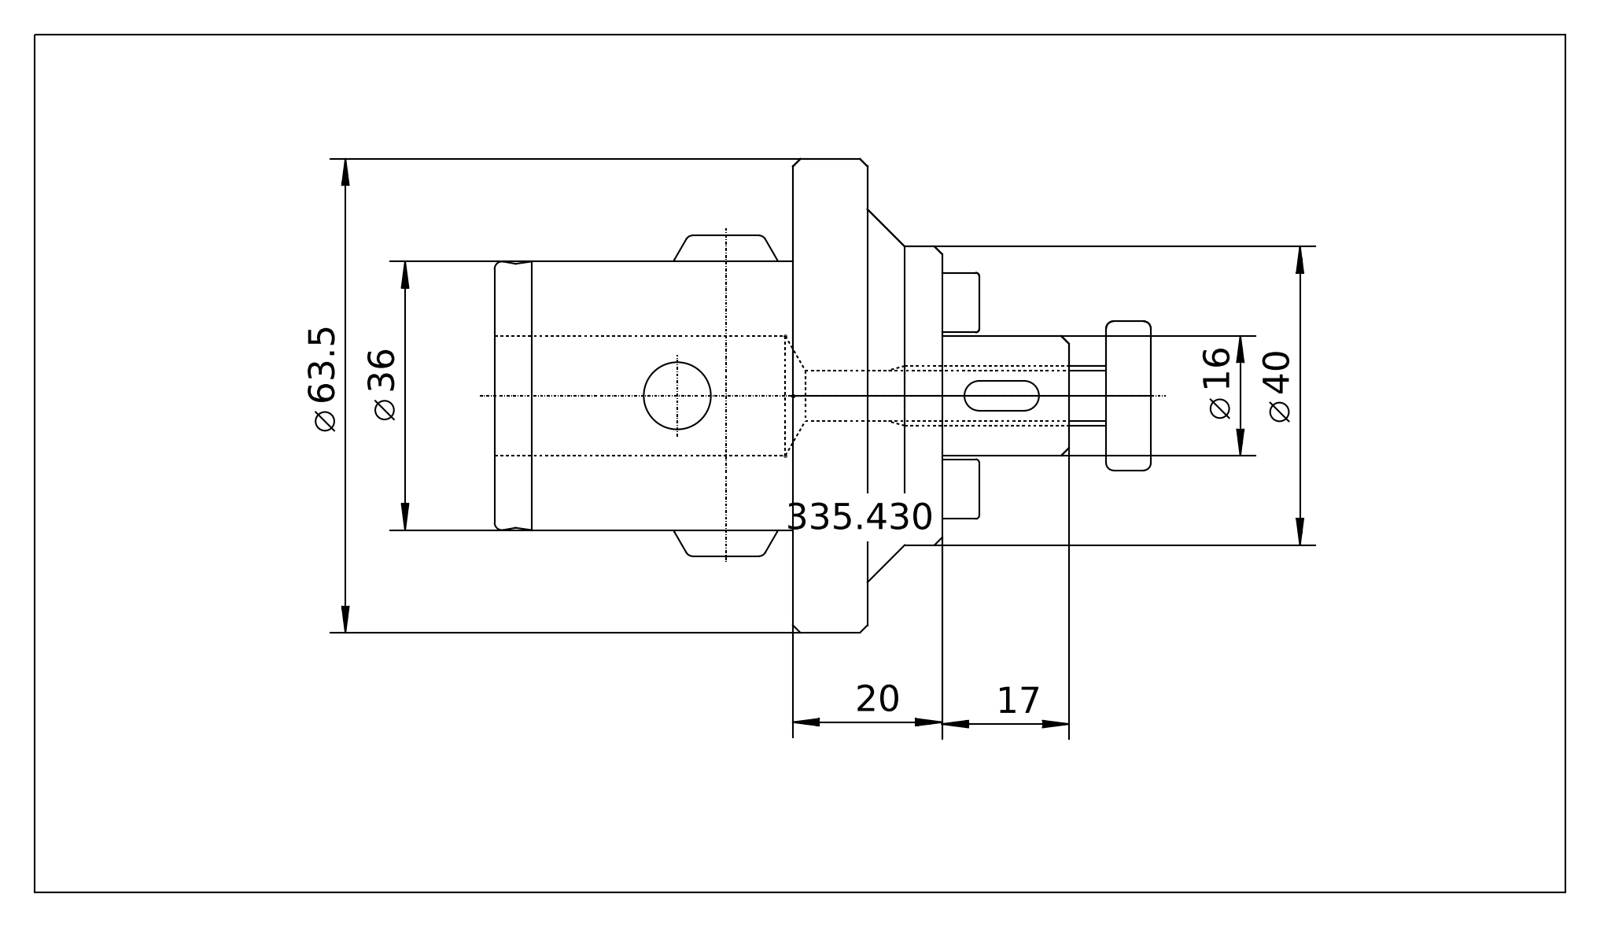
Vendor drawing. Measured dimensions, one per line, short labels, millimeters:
name: 335.430 Kaiser CKS6 X F16|690.703 Kaiser ETL FR16_M8_Standard-1;NONE; 335.430 Kaiser CKS6 X F16|690.703 Kaiser ETL FR16_M8_Standard;NONE; 335.430 Kaiser CKS6 X F16|691.605 Kaiser ETL MST 16 (Paar)_Standard;NONE; 335.430 Kaiser CKS6 X F16|691.600 Kaiser ETL FK 4 X 4_Standard;NONE (+3 more)
written by: ACIS (automotive_design)
unit: mm
bodies: 8 solids, 229 faces (71 planar, 74 cylindrical, 84 other)
size: 86.85 × 63.5 × 63.5
volume: 81 823 mm³; area: 24 643 mm²
holes: 2× ⌀2, 1× ⌀2.5, 1× ⌀3.2, 1× ⌀5.7, 1× ⌀6.75, 1× ⌀8.5, 1× ⌀9, 1× ⌀12, 1× ⌀14, 1× ⌀16, 1× ⌀18.5
bosses: 1× ⌀63.5, 1× ⌀40, 1× ⌀36, 1× ⌀20, 1× ⌀13.93, 1× ⌀10, 1× ⌀8
rounds: 2× R2, 1× R4, 1× R5.5
face distances: 10, 20, 60, 50, 40, 8, 7, 17, 24, 19.35
hole spacings: 19
